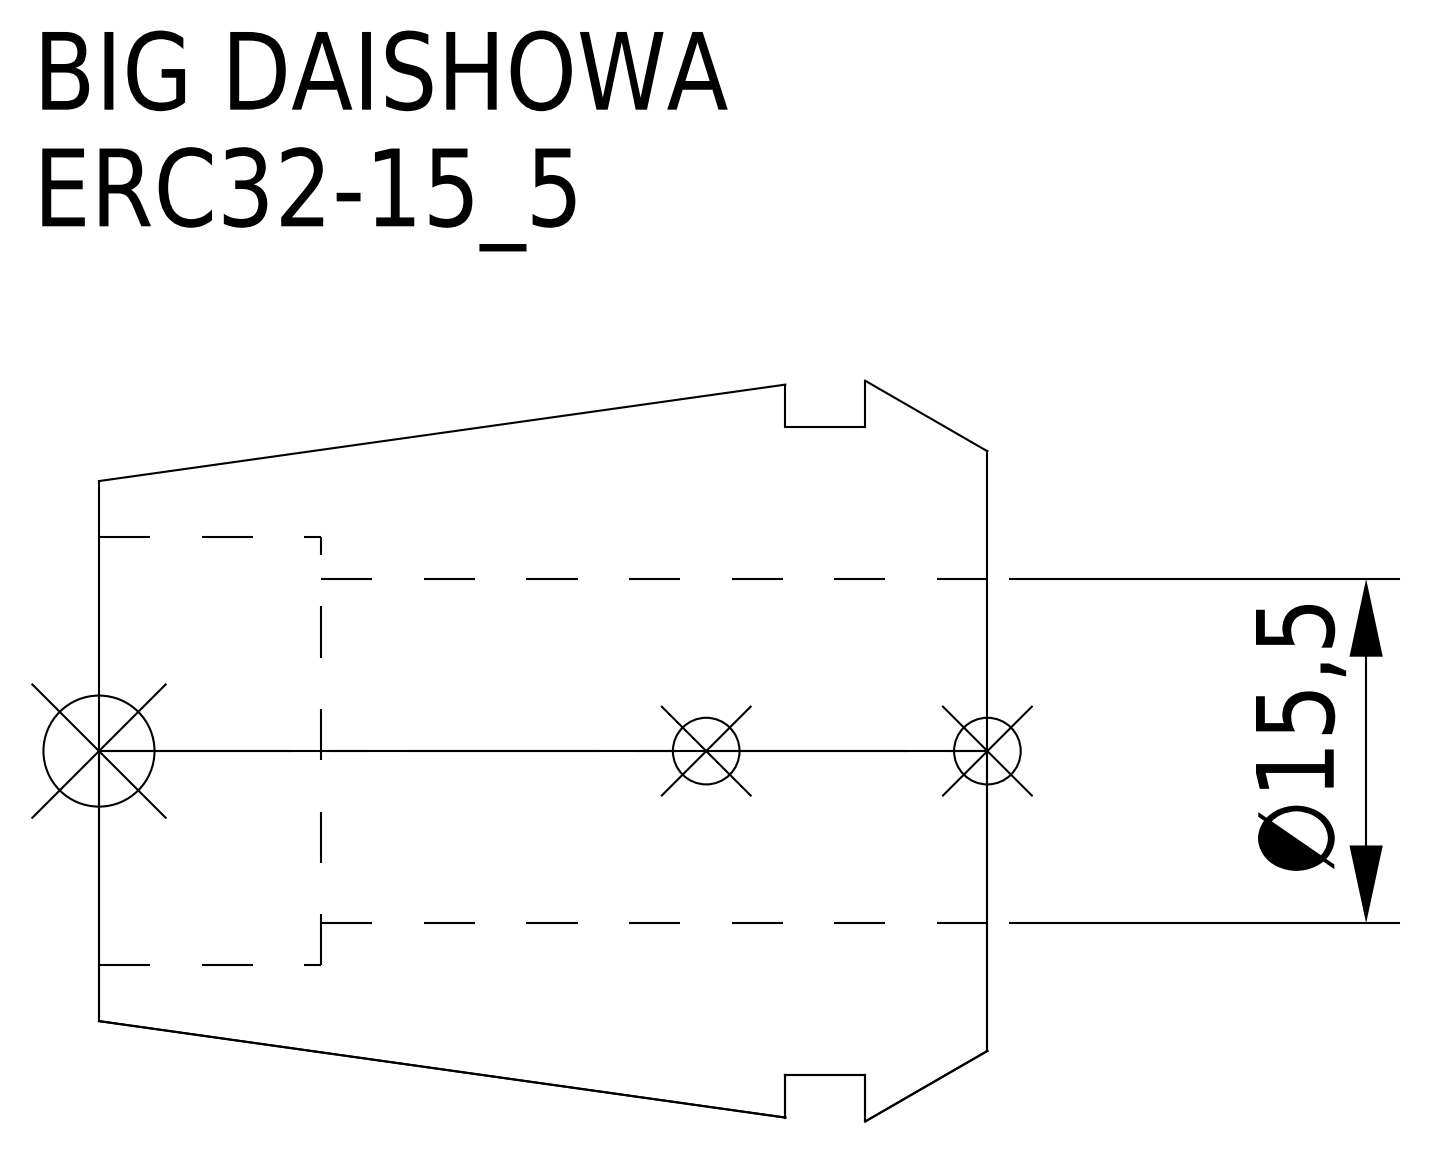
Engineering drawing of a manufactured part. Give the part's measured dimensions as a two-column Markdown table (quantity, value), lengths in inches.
| quantity | value |
| --- | --- |
| part name | ERC32-15_5 |
| STEP written by | CREO PARAMETRIC BY PTC INC, 2016380 (AUTOMOTIVE_DESIGN) |
| units | inches |
| bodies | 1 solid, 15 faces (5 planar, 6 cylindrical, 4 other) |
| overall size | 1.575 × 1.313 × 1.313 |
| volume | 1.09 in³ |
| surface area | 10.63 in² |
| round holes (diameter × count) | 0.61 × 1, 0.76 × 1 |
| round bosses / shafts (diameter × count) | 1.15 × 1 |
| main face-to-face distances | 0.217, 0.358, 0.142, 1.575, 1.358, 1.217, 1.181, 0.965, 0.823, 0.394 |
